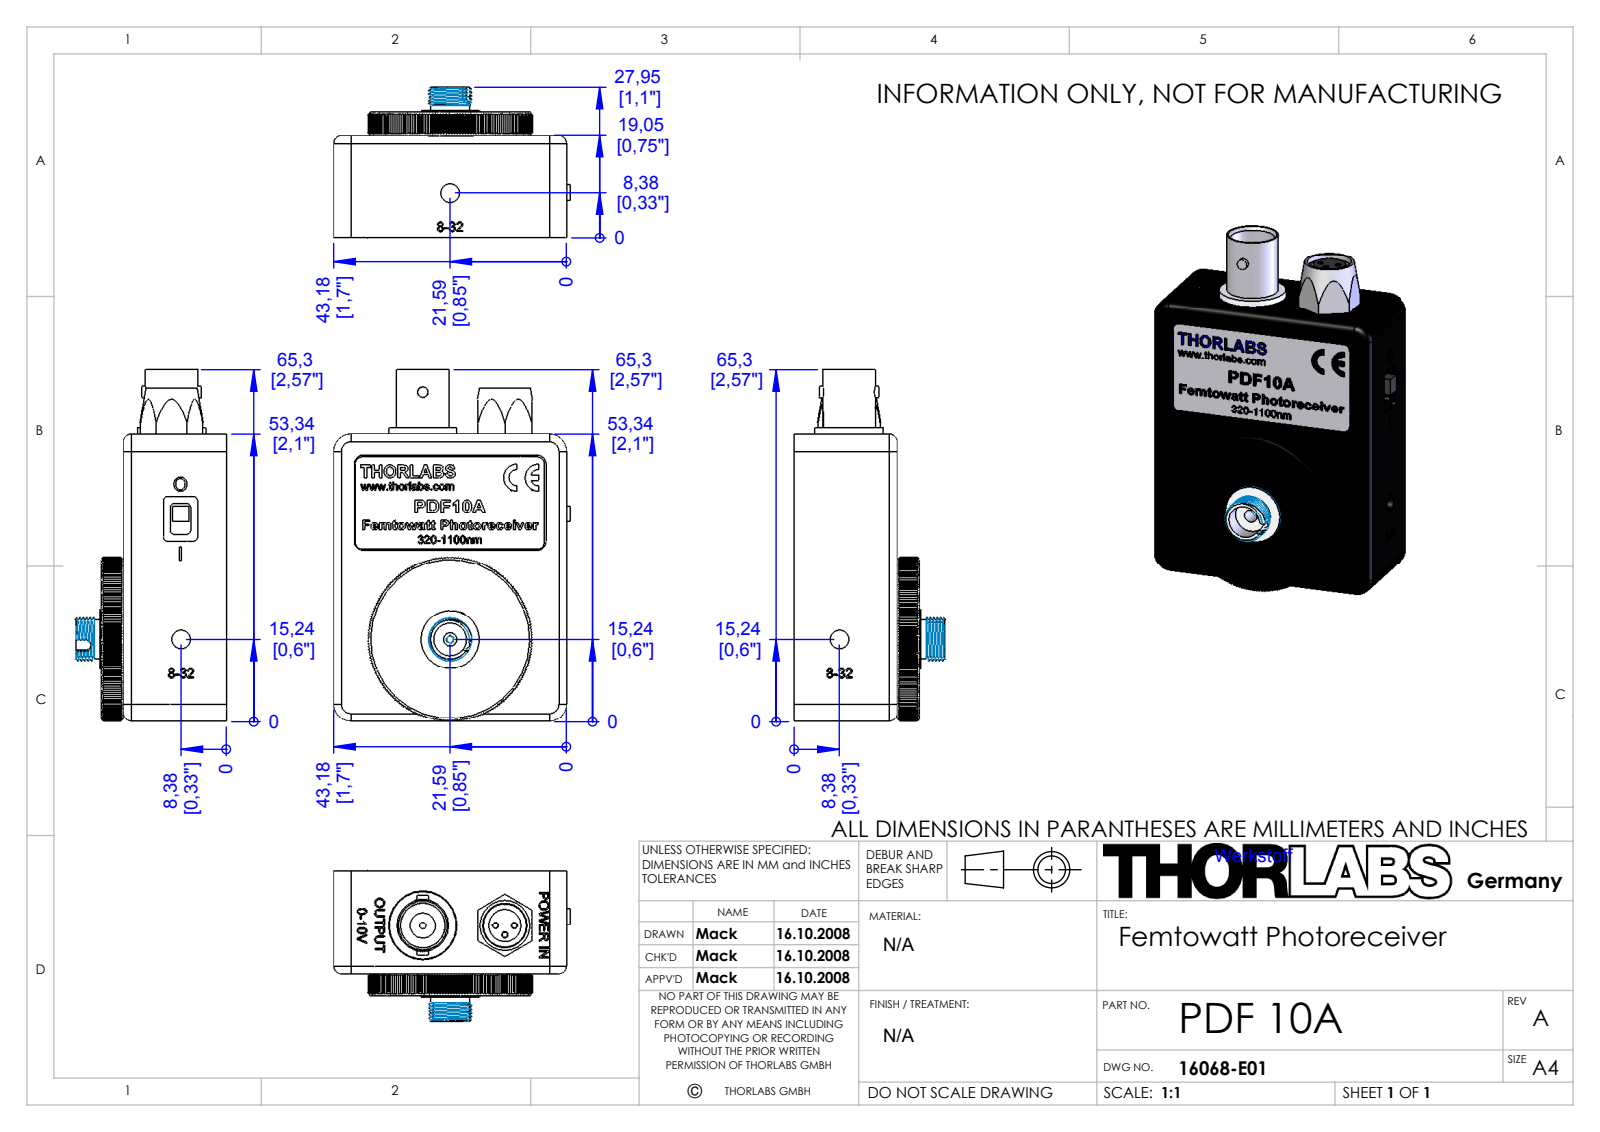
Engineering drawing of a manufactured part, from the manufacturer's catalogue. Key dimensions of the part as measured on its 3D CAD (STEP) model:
Part name (STEP PRODUCT): Schalter-01_Off; S2386-18K-Hamamatsu_Standard; M0092-0430-0A-Deckel; 16068-E01 (+6 more)
STEP written by: SolidWorks 2008 (CONFIG_CONTROL_DESIGN)
Units: millimetres
Bodies: 8 solids, 2376 faces (1275 planar, 440 cylindrical, 661 other)
Overall size (bounding box): 65.3 × 43.84 × 27.95
Volume: 21 009 mm³ · Surface area: 26 268 mm²
Round holes (diameter × count): ⌀1.6 ×7, ⌀1 ×5, ⌀2.4 ×4, ⌀0.71 ×3, ⌀2.44 ×3, ⌀1.27 ×2, ⌀3.45 ×2, ⌀1.32 ×1, ⌀2.5 ×1, ⌀3 ×1, ⌀3.81 ×1, ⌀4.2 ×1
Round bosses / shafts (diameter × count): ⌀0.51 ×6, ⌀0.45 ×2, ⌀26.29 ×1, ⌀13.5 ×1, ⌀12.45 ×1, ⌀10.92 ×1, ⌀10.79 ×1, ⌀9.6 ×1
Partial cylindrical surfaces — rounded edges, fillets, slot ends (radius × count): R3.17 ×32, R3.3 ×12, R0.8 ×10, R0.79 ×8, R2.41 ×8, R1.27 ×4, R1.4 ×4, R1.59 ×3
Main face-to-face distances: 1.59, 2.54, 0.8, 12.28, 10.69, 1.27, 11.48, 9.89, 6.26, 1.78
Hole centre spacings: 1.75, 2.54, 1.27, 2.47, 2.73, 2.94, 3.59, 18.28
